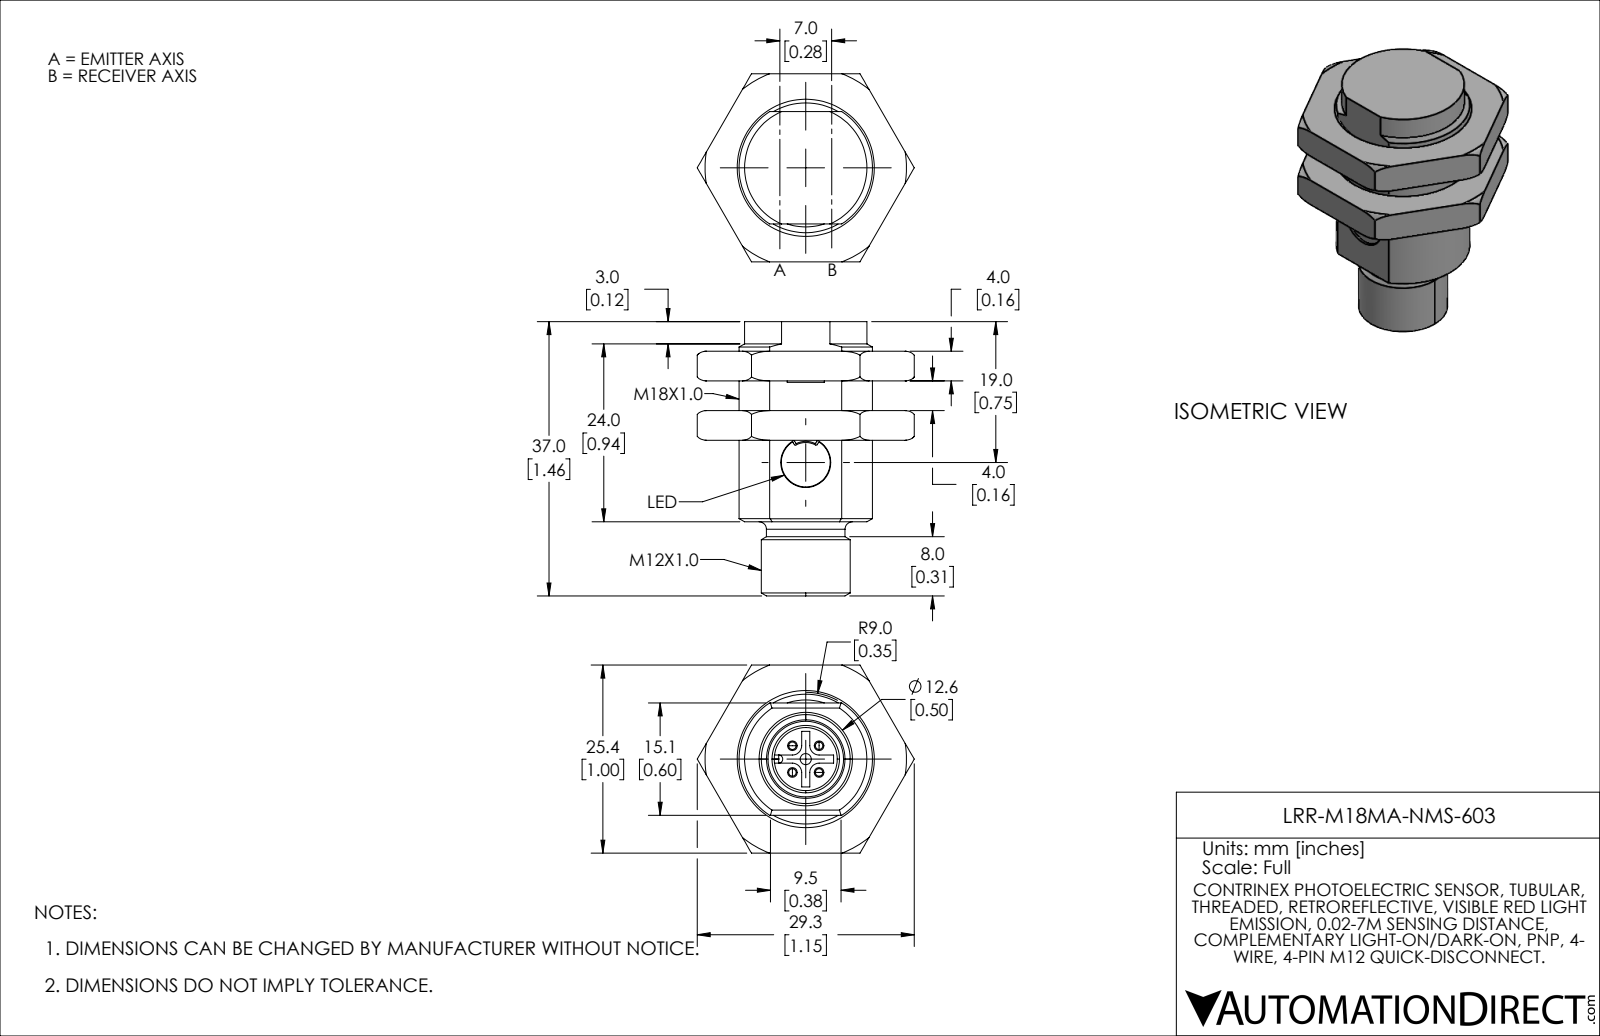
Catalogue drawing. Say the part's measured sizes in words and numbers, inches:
The part is named "LRR-M18MA-NMS-603". Its 3-D file was written by "SolidWorks 2021 (AUTOMOTIVE_DESIGN)". It is 3 solids with 176 faces: 65 planar, 50 cylindrical and 61 other. Overall it measures 1.457 by 1.153 by 0.998 inches. Its volume is 0.572 cubic inches and its surface area 7.737 square inches. Round holes: 1 of diameter 0.059, 1 of diameter 0.266, 1 of diameter 0.335, 1 of diameter 0.689. Round bosses or shafts: 4 of diameter 0.039, 1 of diameter 0.472, 1 of diameter 0.417. Partial cylindrical surfaces (rounded edges, fillets, slot ends): 4 of radius 0.004, 4 of radius 0.006, 4 of radius 0.049, 2 of radius 0.02, 1 of radius 0.022, 1 of radius 0.106, 1 of radius 0.112, 1 of radius 0.325. The main face-to-face distances are 0.157, 0.315, 0.472, 0.998, 0.201, 0.798, 0.597, 0.63, 0.433, 0.591.
